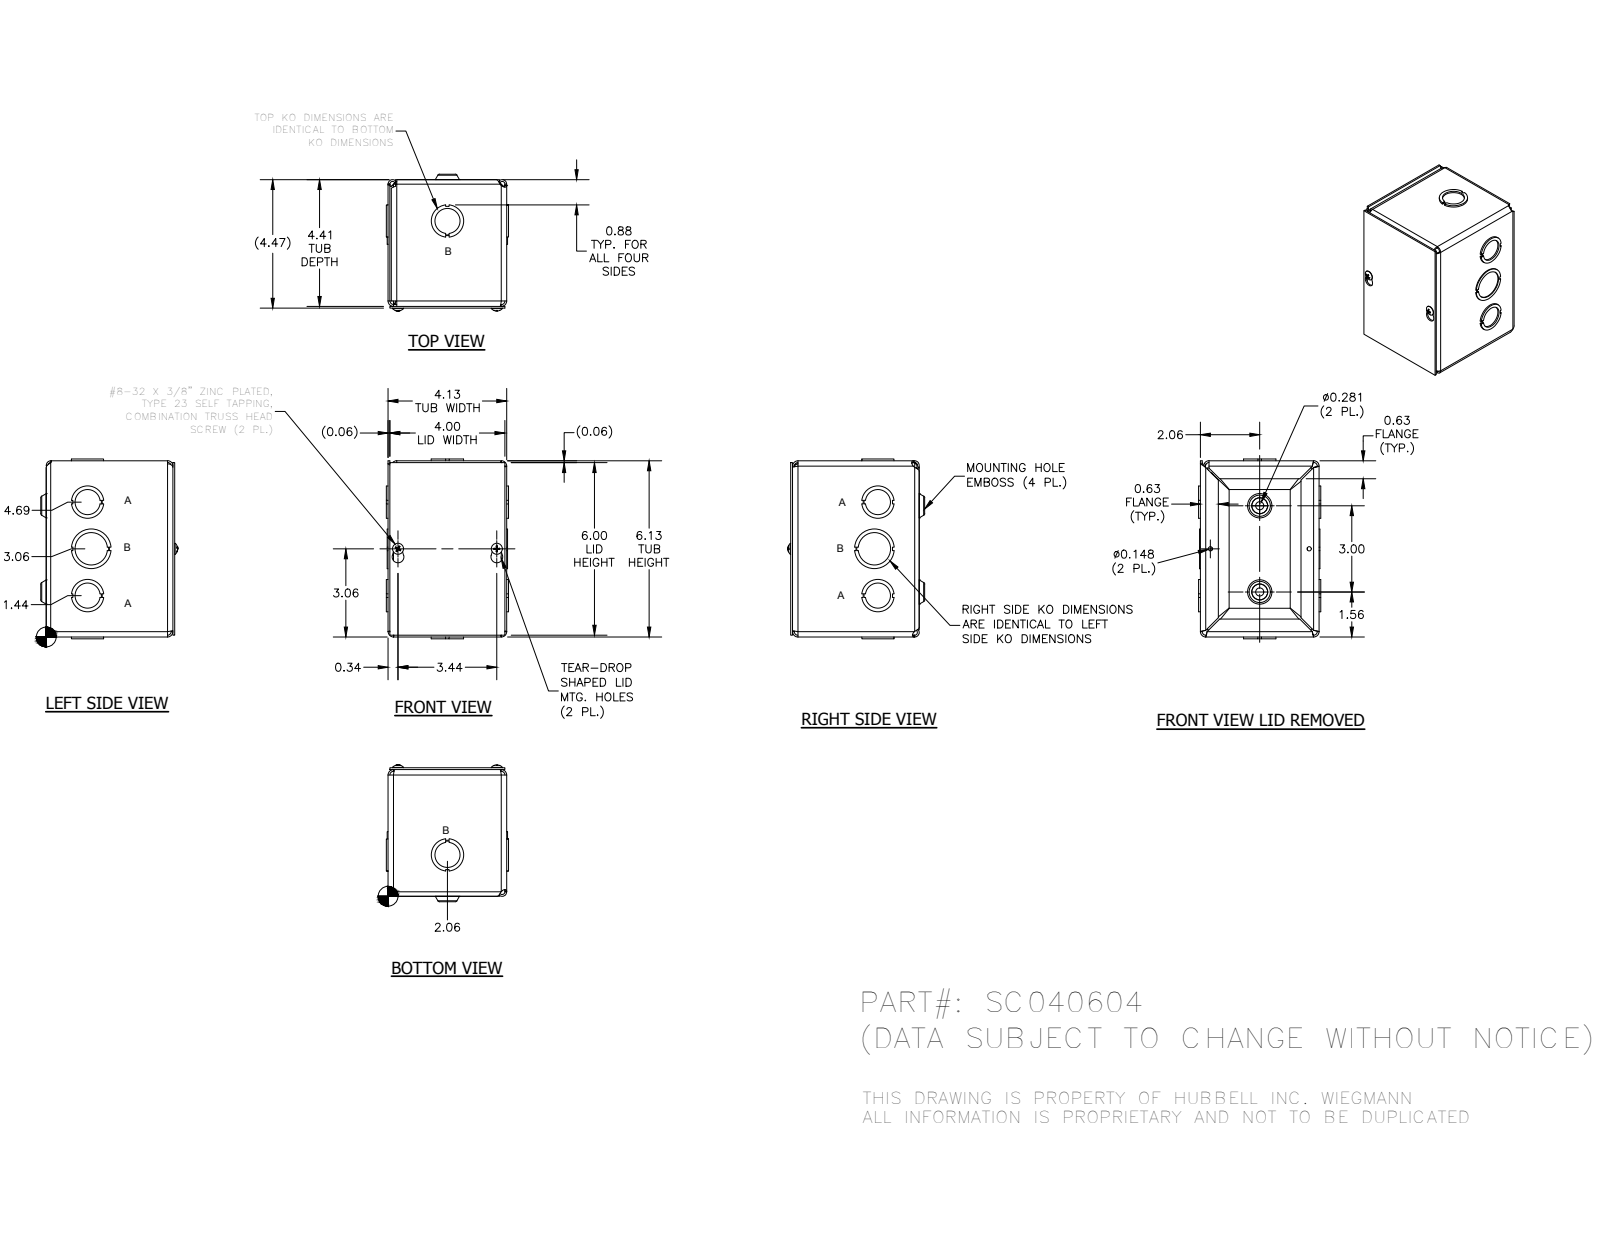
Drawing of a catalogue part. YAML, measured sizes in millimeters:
part_name: "SC0406BKP; SC040604WRA; SC0406LID; 34056 (+1 more)"
step_written_by: "Autodesk Inventor 2014 (AUTOMOTIVE_DESIGN)"
units: millimeters
bodies: {solids: 16, faces: 507, planar: 288, cylindrical: 101, other: 118}
overall_size: [158.72, 120.78, 107.92]
round_holes:
  - {diameter: 28.57, count: 4}
  - {diameter: 22.22, count: 3}
  - {diameter: 3.76, count: 2}
  - {diameter: 7.14, count: 2}
  - {diameter: 34.92, count: 1}
round_bosses_or_shafts:
  - {diameter: 9.75, count: 2}
  - {diameter: 4.17, count: 2}
partial_cylinders:
  - {radius: 3.17, count: 10}
  - {radius: 4.75, count: 8}
  - {radius: 1.4, count: 4}
  - {radius: 1.57, count: 4}
  - {radius: 2.38, count: 4}
  - {radius: 2.97, count: 4}
  - {radius: 3.15, count: 4}
  - {radius: 3.96, count: 4}
face_to_face_distances: [1.57, 110.32, 1.58, 154, 111.89, 104.78, 103.2, 103.21, 101.63, 1.59]
hole_center_spacings: [57.94, 57.95, 41.39, 41.4, 76.2, 82.55, 87.31]
